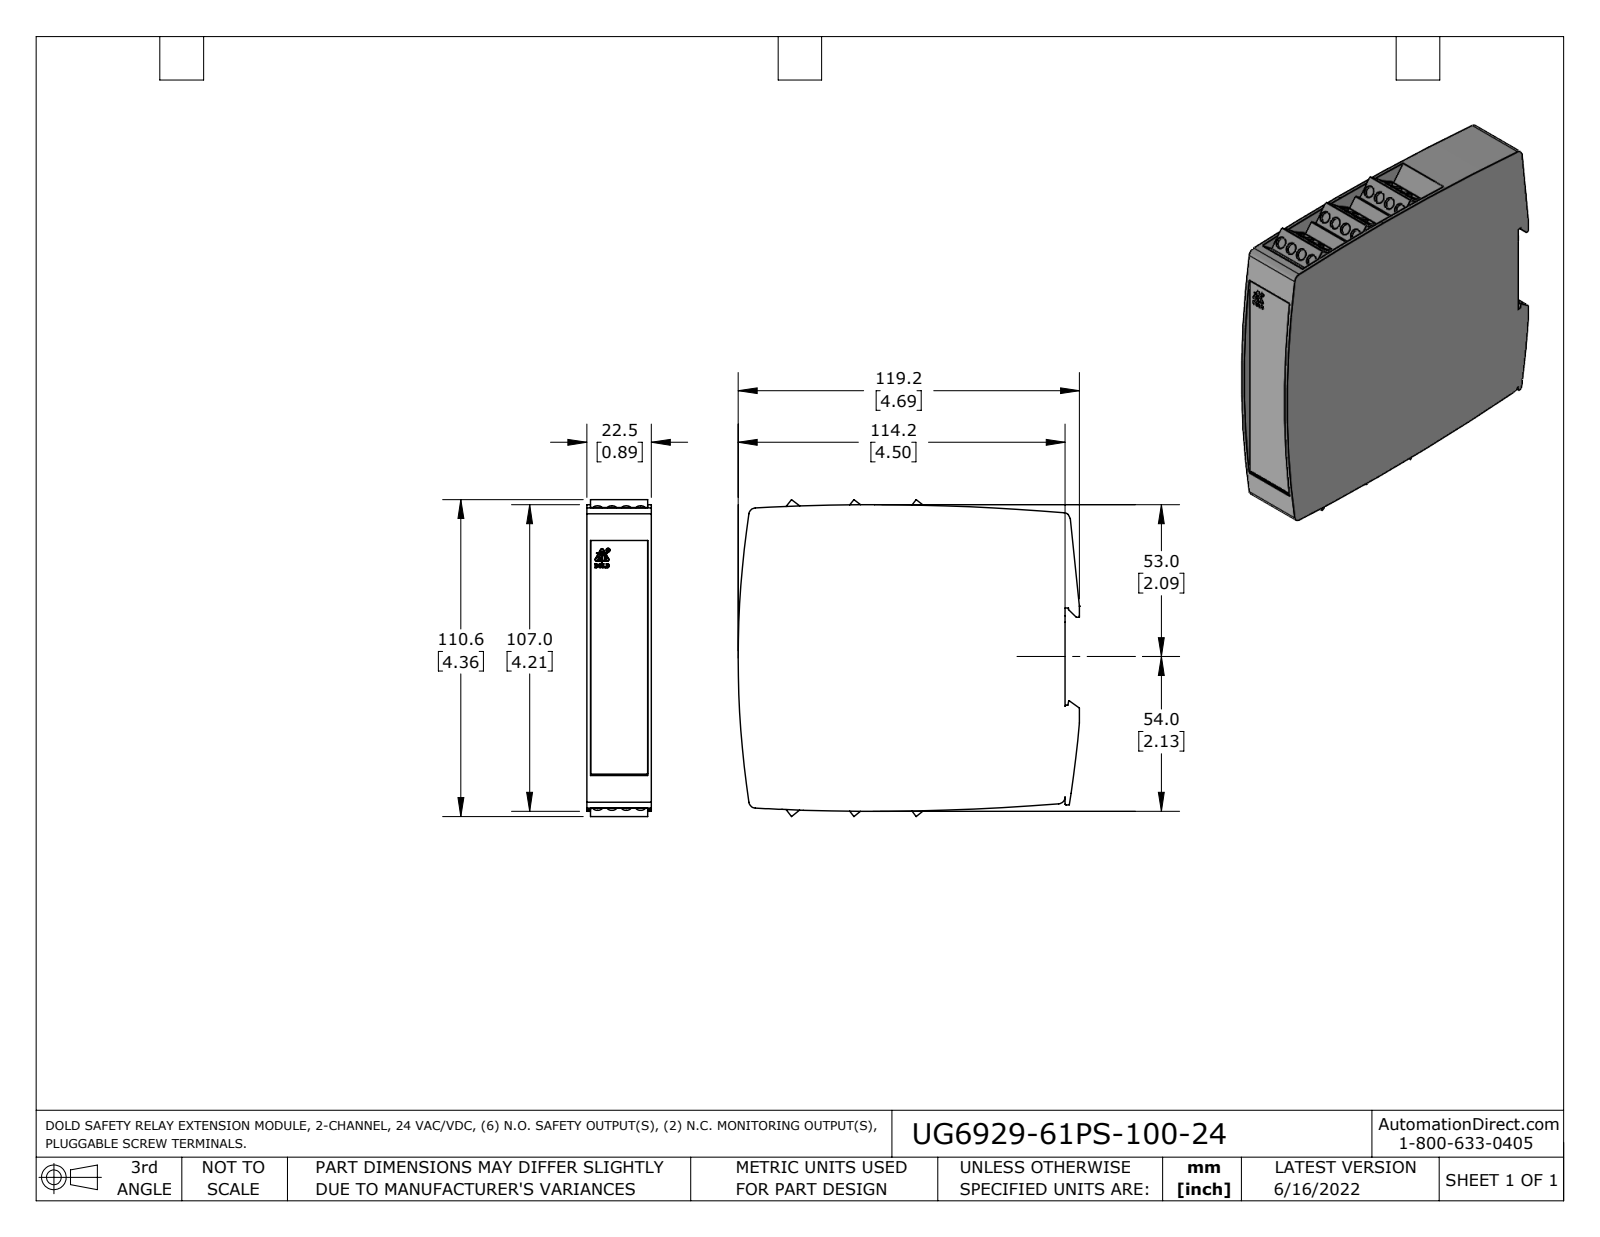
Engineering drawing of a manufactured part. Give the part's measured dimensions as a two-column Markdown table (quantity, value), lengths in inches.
| quantity | value |
| --- | --- |
| part name | UG6929-61PS-100-24 |
| STEP written by | SolidWorks 2021 (AUTOMOTIVE_DESIGN) |
| units | inches |
| bodies | 1 solid, 666 faces (570 planar, 95 cylindrical, 1 other) |
| overall size | 4.693 × 4.355 × 0.886 |
| volume | 16 in³ |
| surface area | 58.45 in² |
| round holes (diameter × count) | 0.157 × 24, 0.053 × 1 |
| round bosses / shafts (diameter × count) | 0.049 × 1 |
| partial cylindrical surfaces (radius × count) | 0.004 × 12, 0.012 × 12, 0.094 × 7, 0.005 × 6, 0.004 × 4, 31.496 × 4, 0.021 × 3, 0.012 × 2 |
| main face-to-face distances | 0.886, 0.049, 0.837, 0.675, 4.379, 0.528, 0.787, 0.528, 1.056, 1.35 |
| hole center spacings | 0.197, 0.394, 0.563, 0.563, 1.074, 0.528, 0.528, 0.658 |
